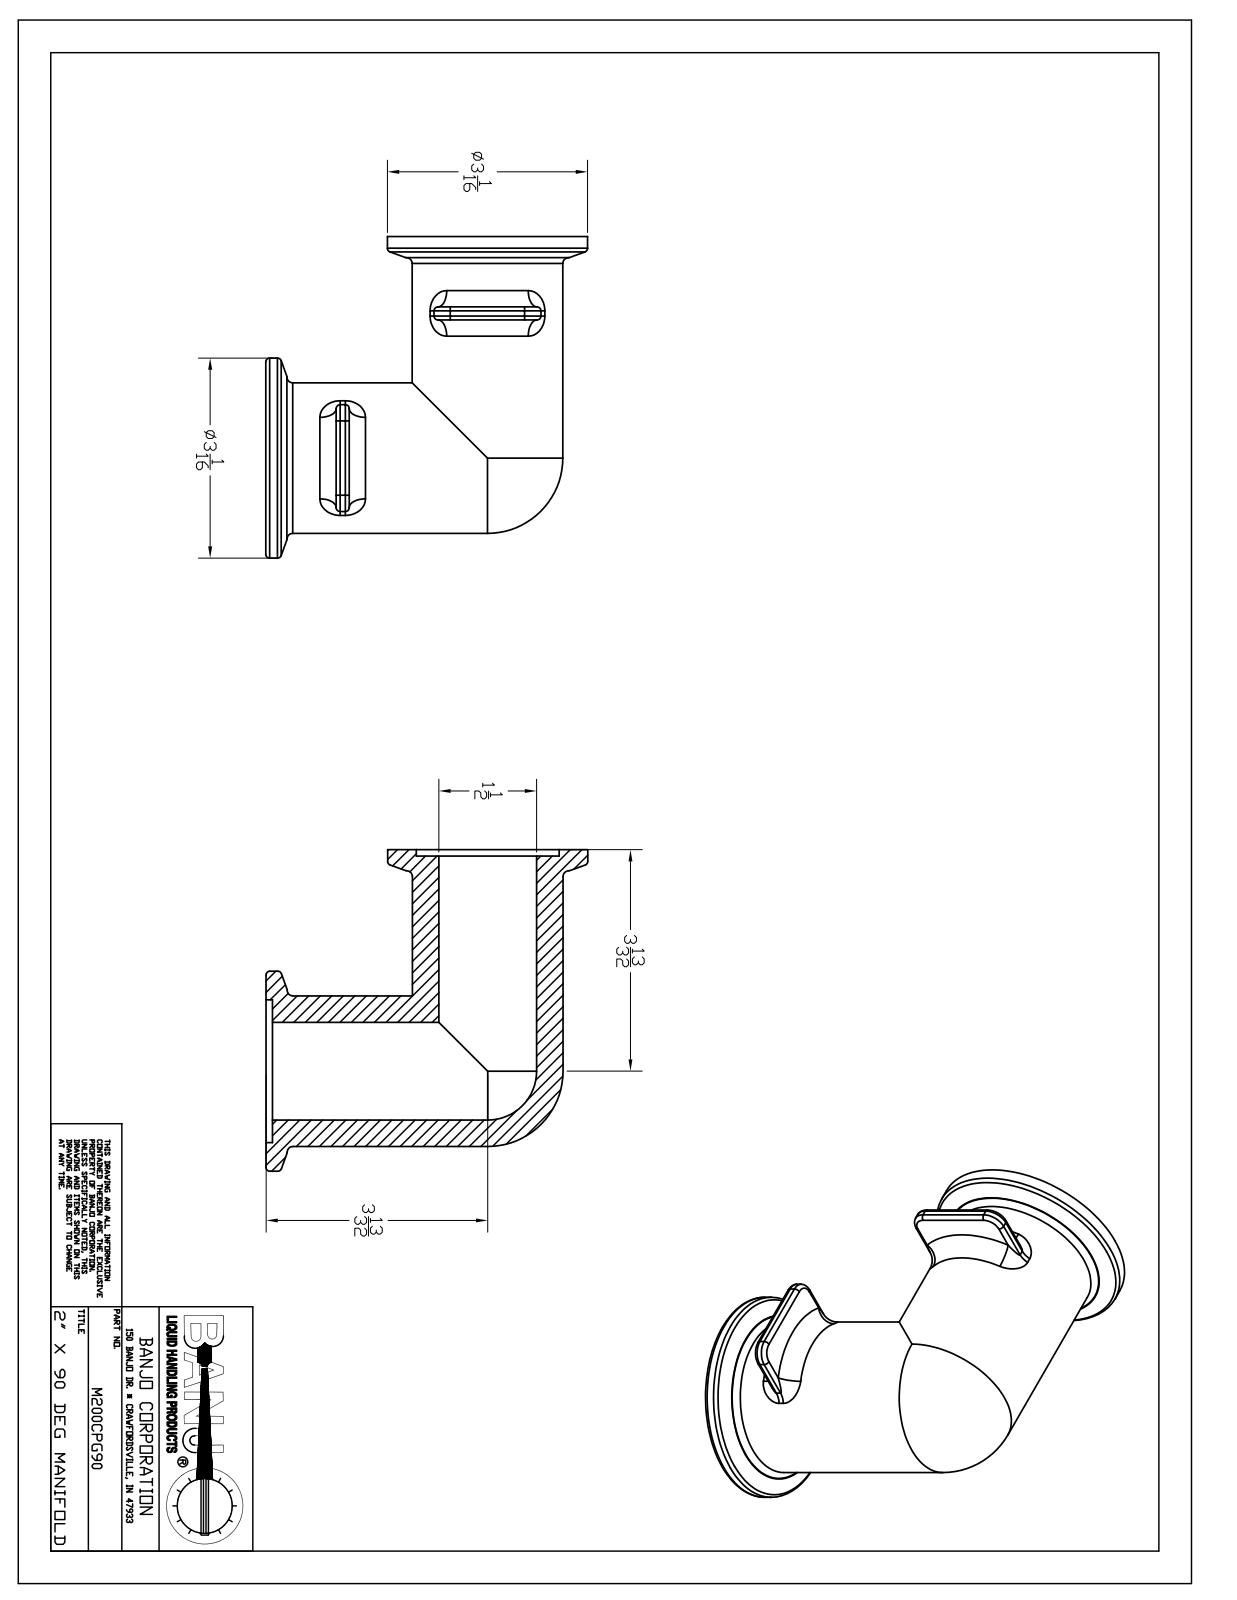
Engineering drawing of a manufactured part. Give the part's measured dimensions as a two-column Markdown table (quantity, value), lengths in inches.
| quantity | value |
| --- | --- |
| part name | M200CPG90 |
| STEP written by | Autodesk Inventor 2014 (AUTOMOTIVE_DESIGN) |
| units | inches |
| bodies | 1 solid, 457 faces (139 planar, 71 cylindrical, 247 other) |
| overall size | 4.935 × 4.935 × 3.315 |
| volume | 18.16 in³ |
| surface area | 101.6 in² |
| round holes (diameter × count) | 1.5 × 2, 2.19 × 2 |
| round bosses / shafts (diameter × count) | 3.07 × 2, 2.31 × 2 |
| partial cylindrical surfaces (radius × count) | 0.03 × 12, 0.25 × 8, 1.135 × 2 |
| main face-to-face distances | 0.1, 1.08, 0.98, 1.28, 1.18, 0.2, 2.58, 4.22, 2.48, 4.12 |
